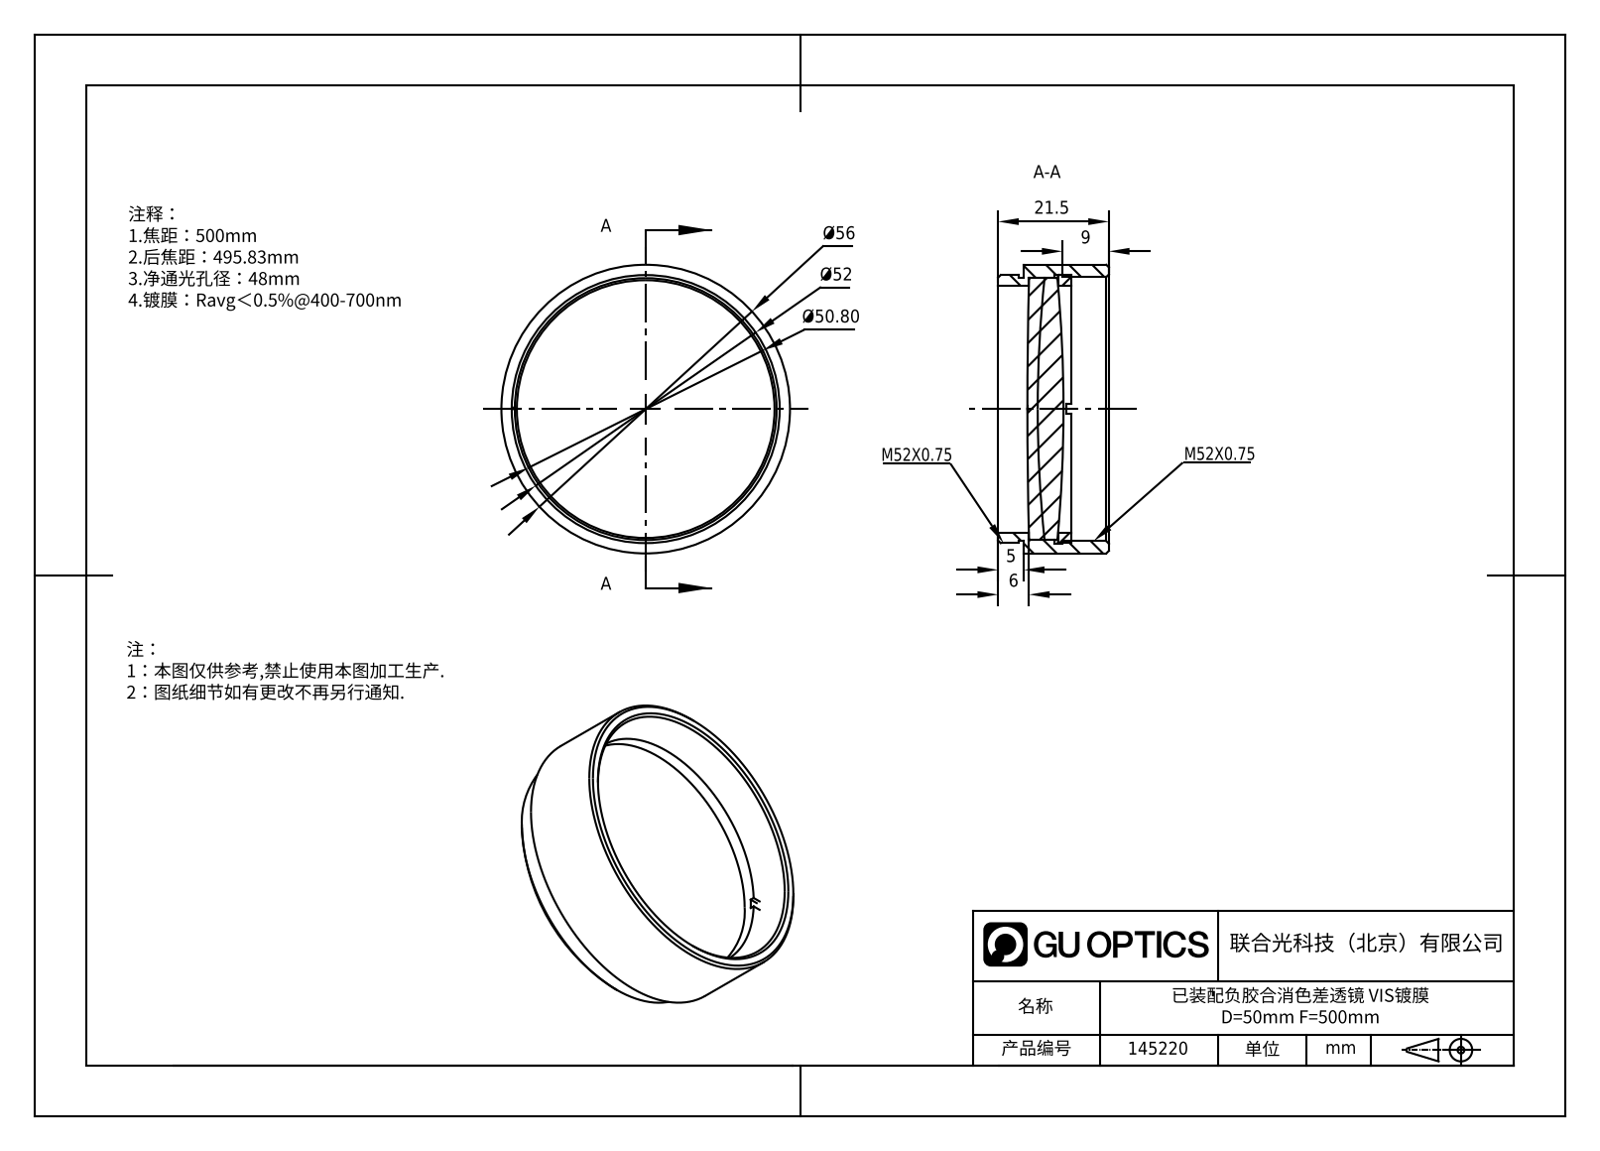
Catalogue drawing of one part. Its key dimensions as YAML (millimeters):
part_name: "M52x0.75ѹȦ; M52x0.75安装环-PN35002-LM508-D1; APD-ML50-500-VIS; GL31-050B-500-VIS_Solidworks"
step_written_by: "SolidWorks 2022 (AUTOMOTIVE_DESIGN)"
units: millimeters
bodies: {solids: 4, faces: 58, planar: 16, cylindrical: 22, other: 20}
overall_size: [56, 56, 21.5]
volume: 21804
surface_area: 18936
round_holes:
  - {diameter: 48, count: 1}
  - {diameter: 51.25, count: 1}
  - {diameter: 52.1, count: 1}
round_bosses_or_shafts:
  - {diameter: 56, count: 1}
  - {diameter: 52, count: 1}
  - {diameter: 51, count: 1}
  - {diameter: 50.8, count: 1}
face_to_face_distances: [5, 6, 9.13, 1, 6.63, 2.5, 11.63, 14.13, 21.5, 16.5]
